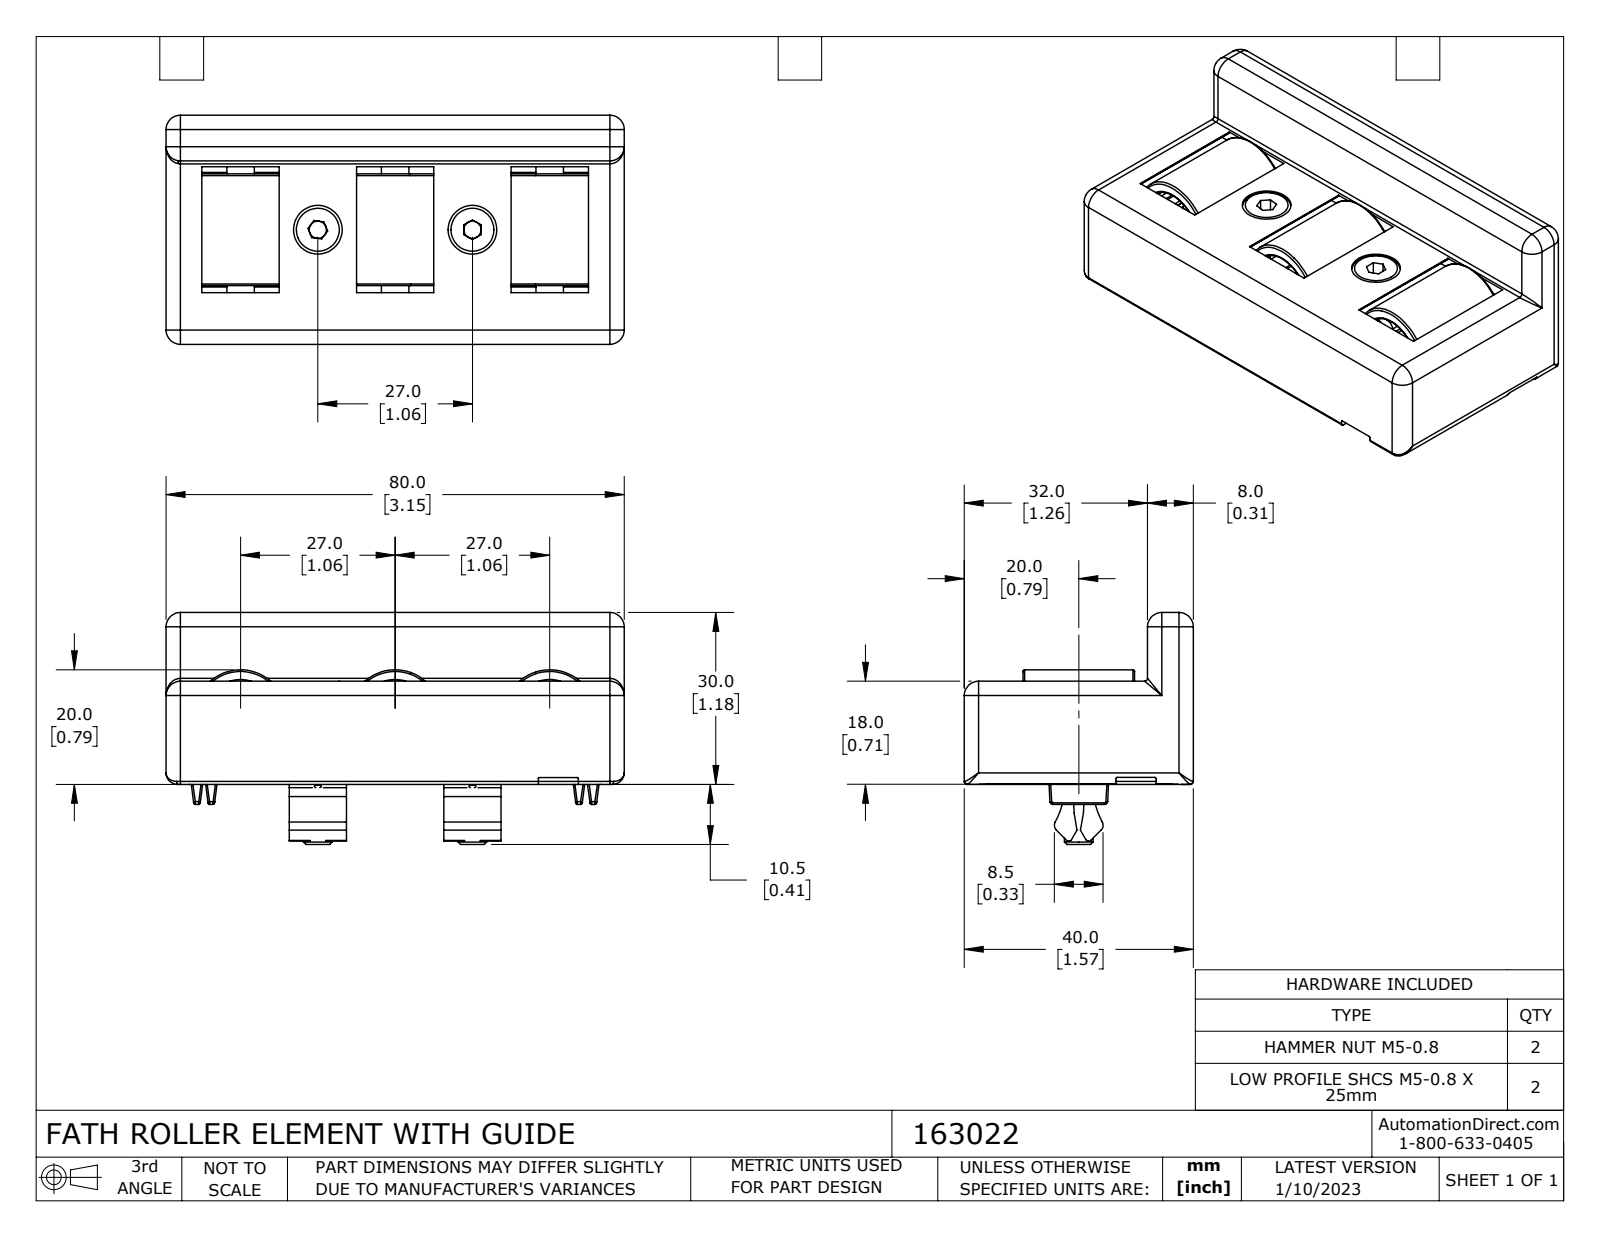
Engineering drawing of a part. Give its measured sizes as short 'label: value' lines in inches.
name: 163022
written by: SolidWorks 2021 (CONFIG_CONTROL_DESIGN)
unit: in
bodies: 9 solids, 1131 faces (572 planar, 395 cylindrical, 164 other)
size: 3.15 × 1.594 × 1.575
volume: 2.713 in³; area: 65.84 in²
holes: 3× ⌀0.472, 2× ⌀0.165, 2× ⌀0.173, 2× ⌀0.197, 2× ⌀0.205, 2× ⌀0.335
bosses: 3× ⌀0.63, 3× ⌀0.189
rounds: 83× R0.02, 28× R0.039, 24× R0.012, 19× R0.098, 18× R0.008, 10× R0.079, 9× R0.053, 2× R0.004
face distances: 0.079, 0.083, 0.63, 1.496, 0.118, 0.071, 0.154, 0.075, 0.551, 1.413
hole spacings: 1.063, 0.335, 1.398, 1.732, 2.126
